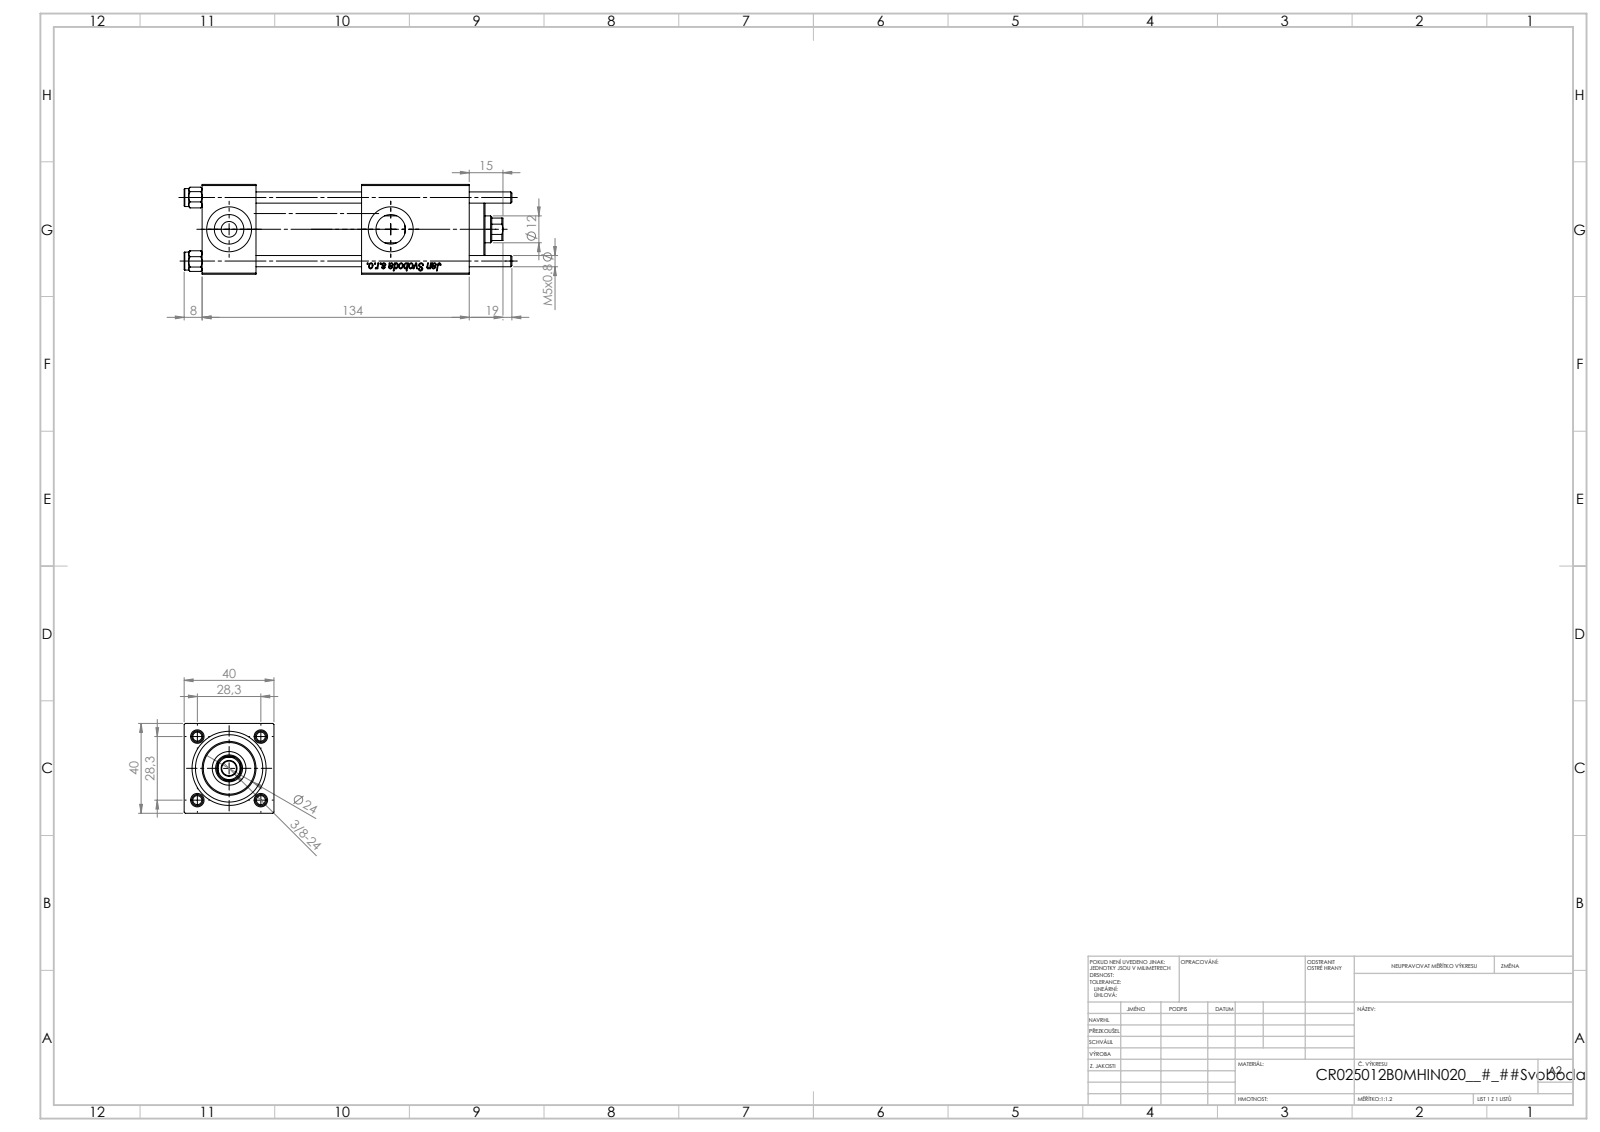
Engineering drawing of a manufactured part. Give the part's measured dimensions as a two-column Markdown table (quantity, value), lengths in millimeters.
| quantity | value |
| --- | --- |
| part name | V215CR_B-1; NUT_M5_B; V215CR_B_TYCINKA; V215_VC_A (+1 more) |
| STEP written by | SolidWorks 2019 (CONFIG_CONTROL_DESIGN) |
| units | millimeters |
| bodies | 11 solids, 1155 faces (429 planar, 78 cylindrical, 648 other) |
| overall size | 146 × 40 × 40 |
| volume | 144 884 mm³ |
| surface area | 58 619 mm² |
| round holes (diameter × count) | 5 × 4, 20 × 3, 7 × 2, 13.16 × 2, 6.5 × 1, 12 × 1, 15 × 1, 25 × 1, 30 × 1 |
| round bosses / shafts (diameter × count) | 8 × 4, 31 × 1, 24 × 1 |
| partial cylindrical surfaces (radius × count) | 5.5 × 1 |
| main face-to-face distances | 40, 24, 90.3, 66.3, 71, 47, 19.3, 119, 95, 48 |
| hole center spacings | 20.01, 28.3, 40.02, 72 |
